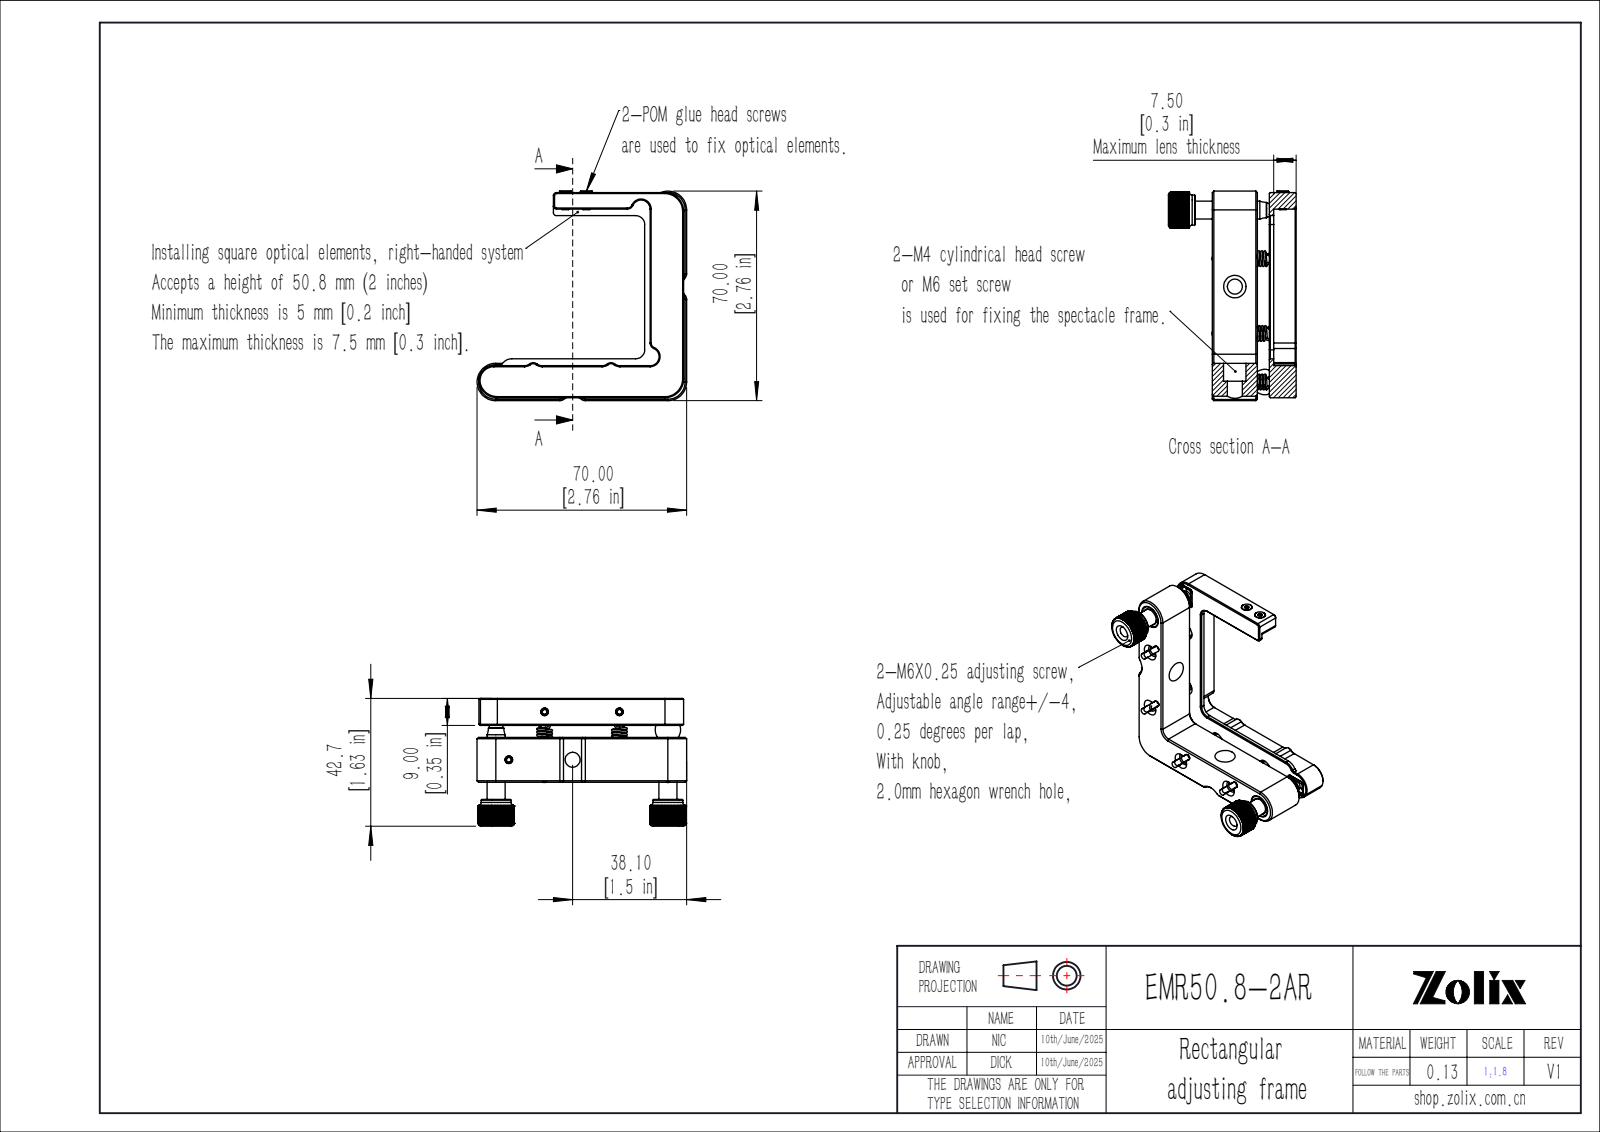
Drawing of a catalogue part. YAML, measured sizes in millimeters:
part_name: "EMR50.8-2AR"
step_written_by: "SolidWorks 2020 (CONFIG_CONTROL_DESIGN)"
units: millimeters
bodies: {solids: 0, faces: 1004, planar: 499, cylindrical: 280, other: 225}
overall_size: [70, 70, 42.71]
round_holes:
  - {diameter: 6, count: 5}
  - {diameter: 3.3, count: 2}
  - {diameter: 5, count: 2}
  - {diameter: 7.5, count: 2}
  - {diameter: 8.6, count: 2}
  - {diameter: 9.8, count: 2}
  - {diameter: 4, count: 1}
  - {diameter: 9.5, count: 1}
  - {diameter: 10, count: 1}
round_bosses_or_shafts:
  - {diameter: 2, count: 4}
  - {diameter: 1.5, count: 4}
  - {diameter: 4, count: 3}
  - {diameter: 2.4, count: 2}
  - {diameter: 10, count: 1}
  - {diameter: 6, count: 1}
  - {diameter: 3, count: 1}
partial_cylinders:
  - {radius: 3, count: 9}
  - {radius: 0.8, count: 8}
  - {radius: 1.1, count: 8}
  - {radius: 2, count: 8}
  - {radius: 6.25, count: 6}
  - {radius: 1, count: 4}
  - {radius: 2.5, count: 2}
  - {radius: 4.83, count: 2}
face_to_face_distances: [9, 12.5, 13, 4, 15, 28, 19, 1, 11.5, 5.5]
hole_center_spacings: [16.2, 25, 41.2, 44.27, 59.64, 70.66, 7, 16.18]
